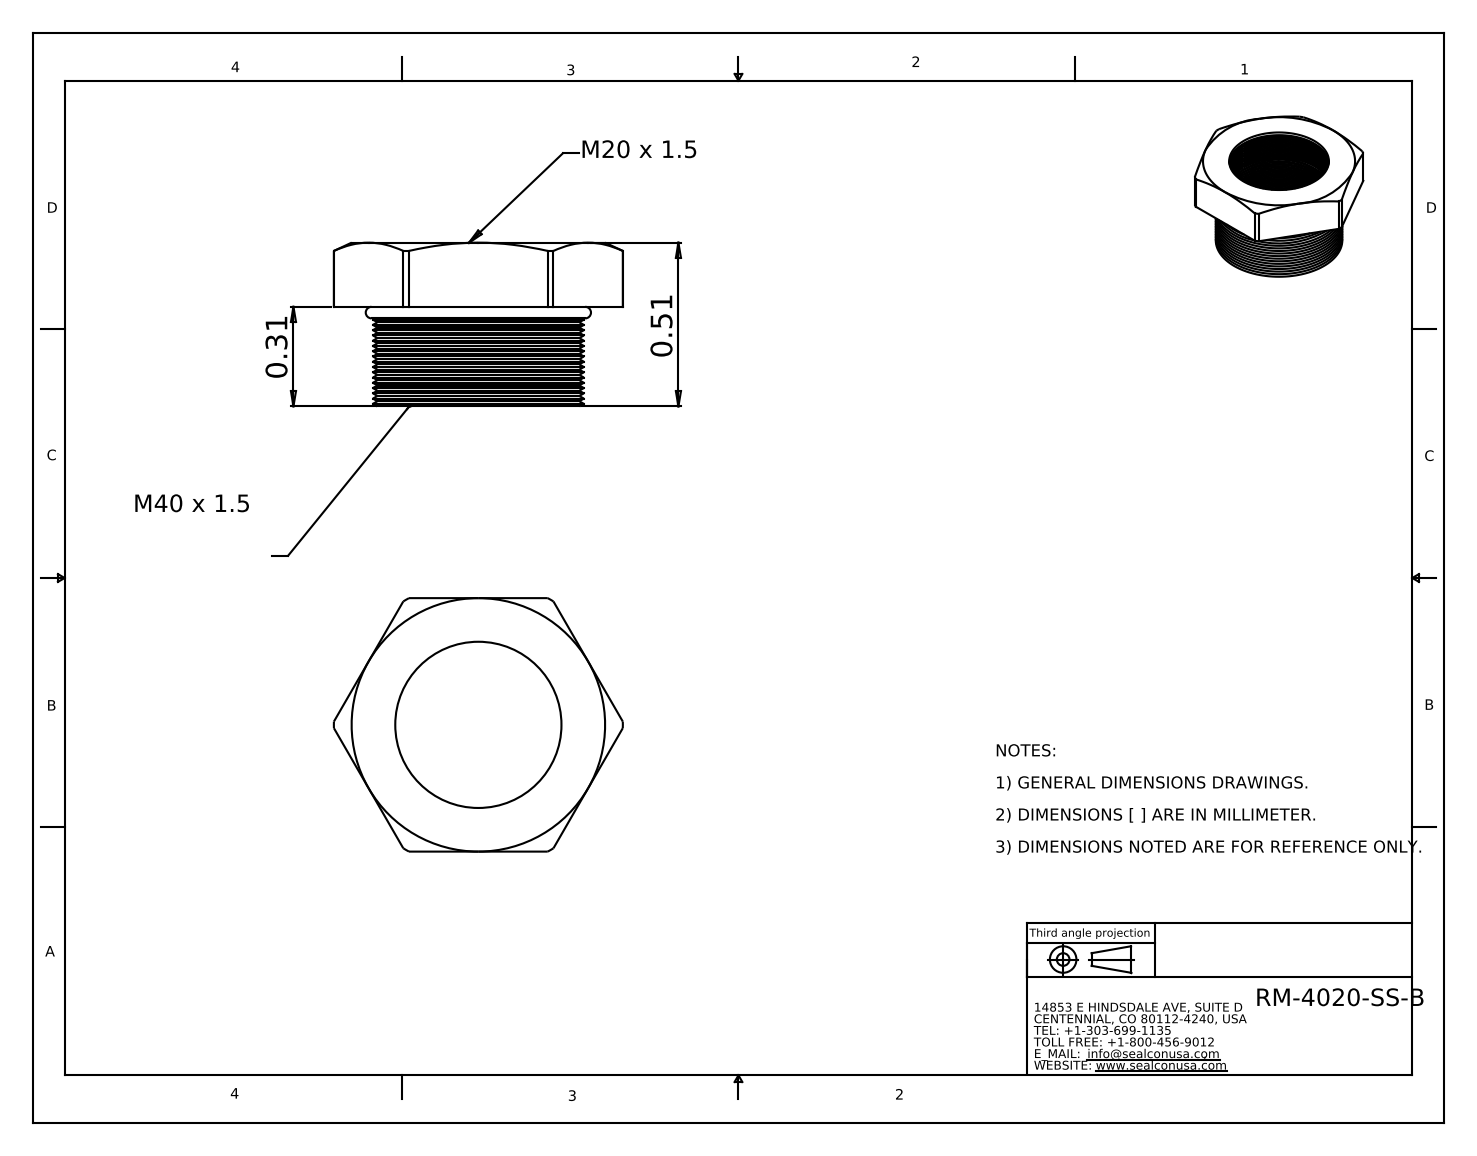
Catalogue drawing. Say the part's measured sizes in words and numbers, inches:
The part is named "RM-4020-SS-B". Its 3-D file was written by "SolidWorks 2008 (CONFIG_CONTROL_DESIGN)". It is 2 solids with 313 faces: 9 planar, 105 cylindrical and 199 other. Overall it measures 0.901 by 0.79 by 0.51 inches. Its volume is 0.1 cubic inches and its surface area 4.242 square inches. Round holes: 1 of diameter 0.518. Round bosses or shafts: 1 of diameter 0.63. Partial cylindrical surfaces (rounded edges, fillets, slot ends): 1 of radius 0.45. The main face-to-face distances are 0.79, 0.2, 0.31, 0.51.
